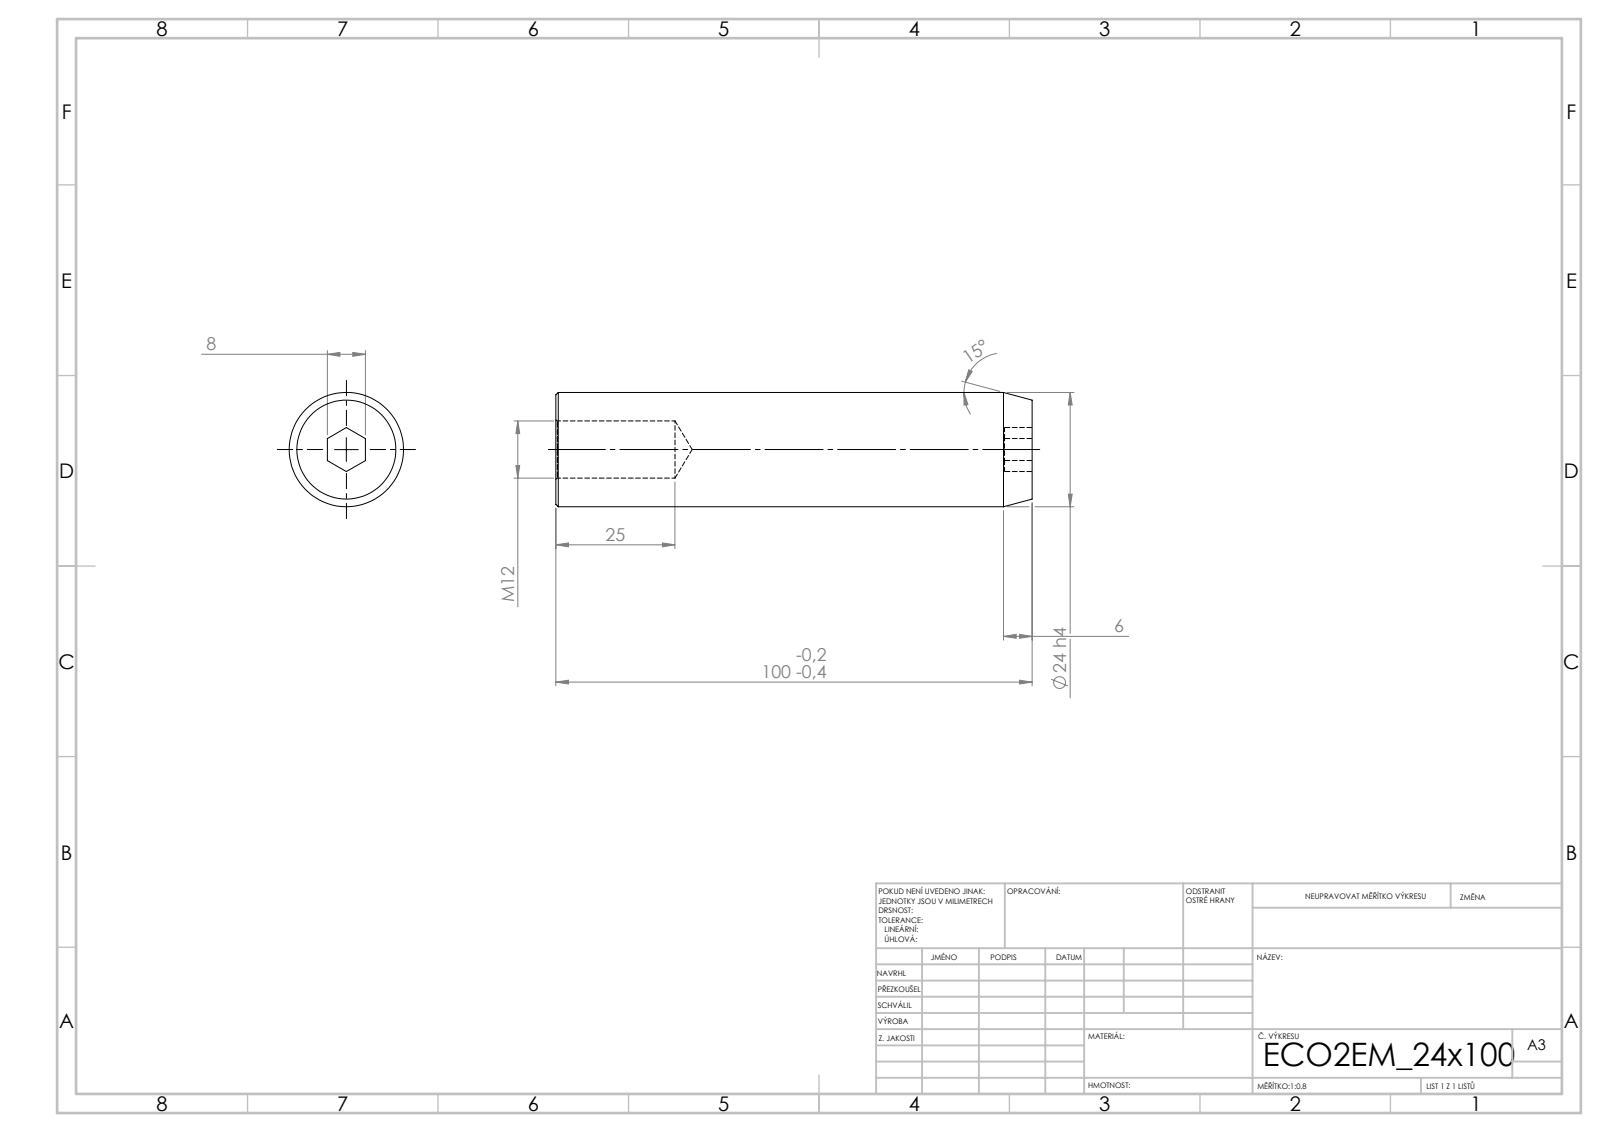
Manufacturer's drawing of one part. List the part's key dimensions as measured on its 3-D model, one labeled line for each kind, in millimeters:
STEP written by: SolidWorks 2019 (CONFIG_CONTROL_DESIGN)
Units: millimetres
Bodies: 1 solid, 21 faces (9 planar, 4 cylindrical, 8 other)
Overall size (bounding box): 100 × 24 × 24
Volume: 41 597 mm³ · Surface area: 9 411 mm²
Round holes (diameter × count): ⌀12 ×1
Round bosses / shafts (diameter × count): ⌀24 ×1
Main face-to-face distances: 100, 8, 5.8, 94.2
